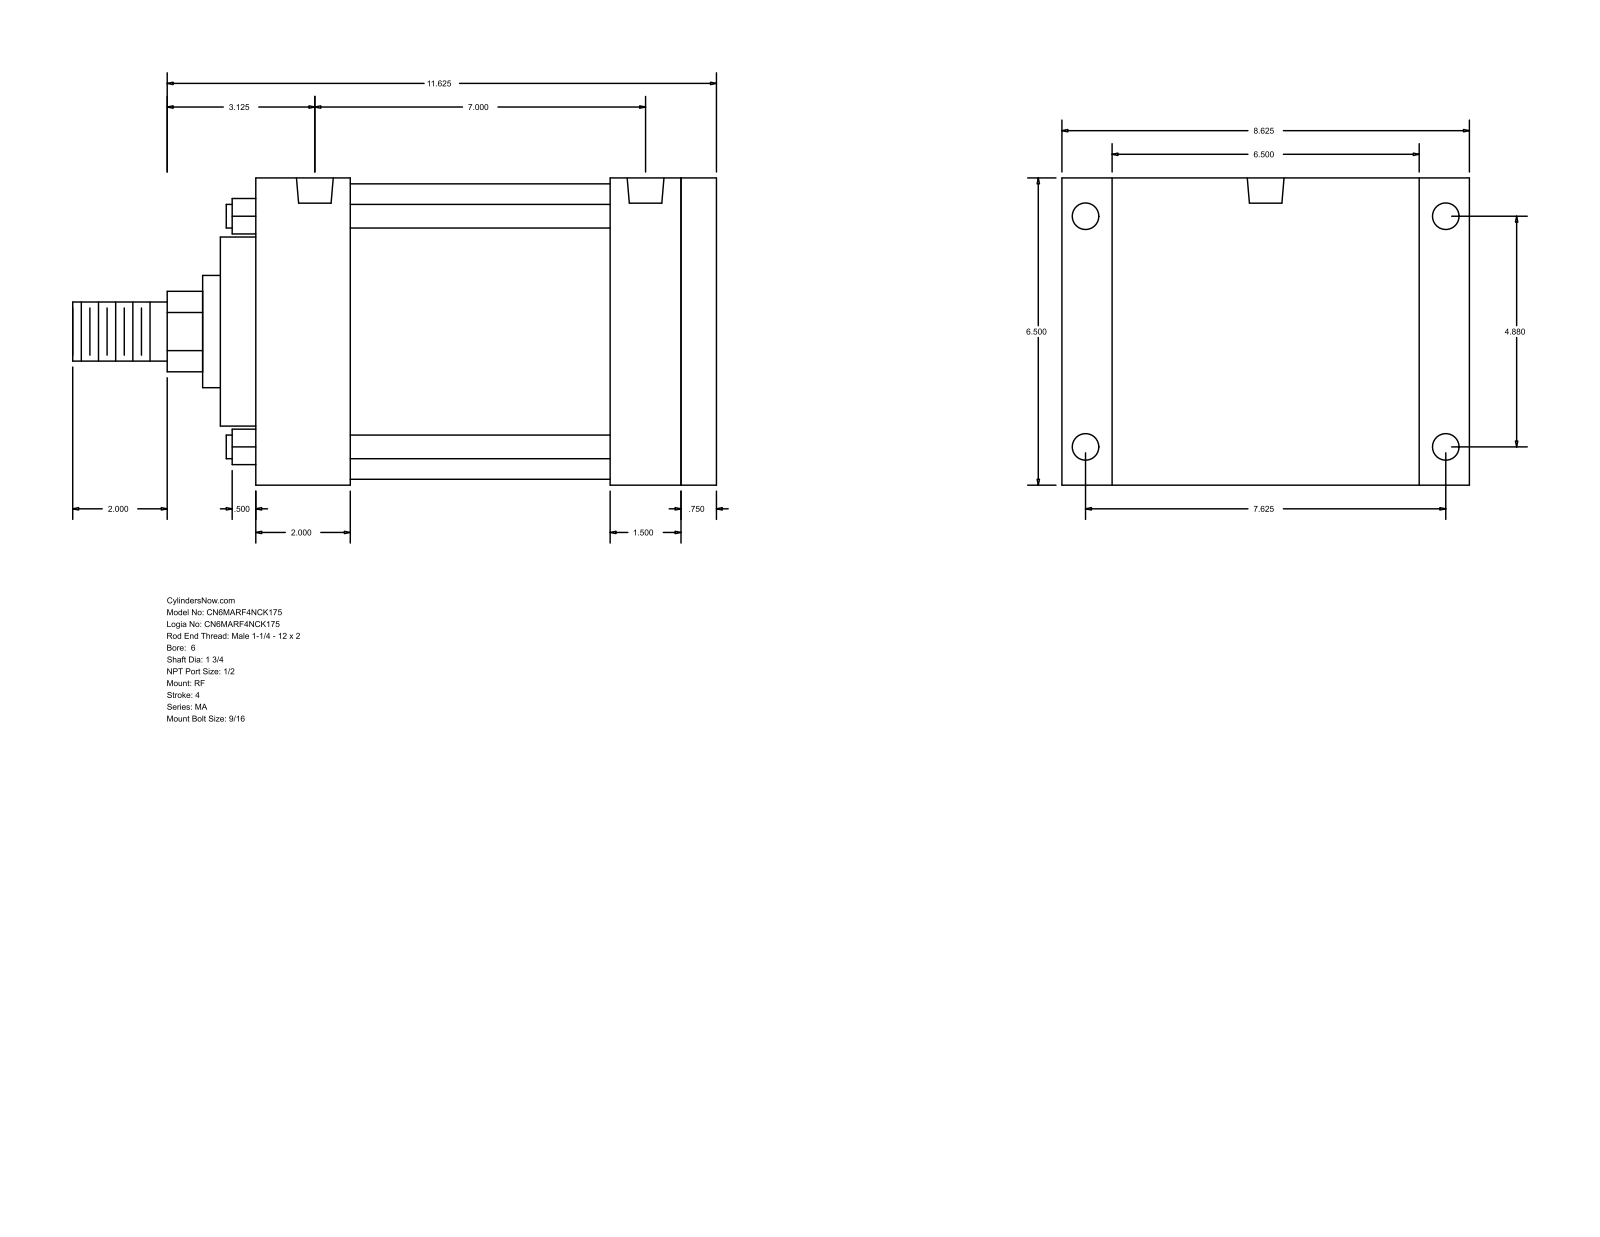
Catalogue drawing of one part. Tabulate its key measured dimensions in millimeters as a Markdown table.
| quantity | value |
| --- | --- |
| part name | MA_RF__0600_1.75 |
| STEP written by | GSSL Pune (CONFIG_CONTROL_DESIGN) |
| units | millimeters |
| bodies | 0 solids, 94 faces (65 planar, 29 cylindrical, 0 other) |
| overall size | 346.07 × 219.07 × 165.1 |
| round holes (diameter × count) | 14.29 × 4, 17.46 × 4, 19.77 × 2 |
| round bosses / shafts (diameter × count) | 12.7 × 4, 158.75 × 1, 101.6 × 1, 60.33 × 1, 44.45 × 1, 31.75 × 1 |
| partial cylindrical surfaces (radius × count) | 21.63 × 1 |
| main face-to-face distances | 165.1, 247.65, 19.04, 228.61, 50.8, 19.05, 177.81, 196.85, 190.5, 139.7 |
| hole center spacings | 123.96, 177.8, 193.68, 229.95 |
